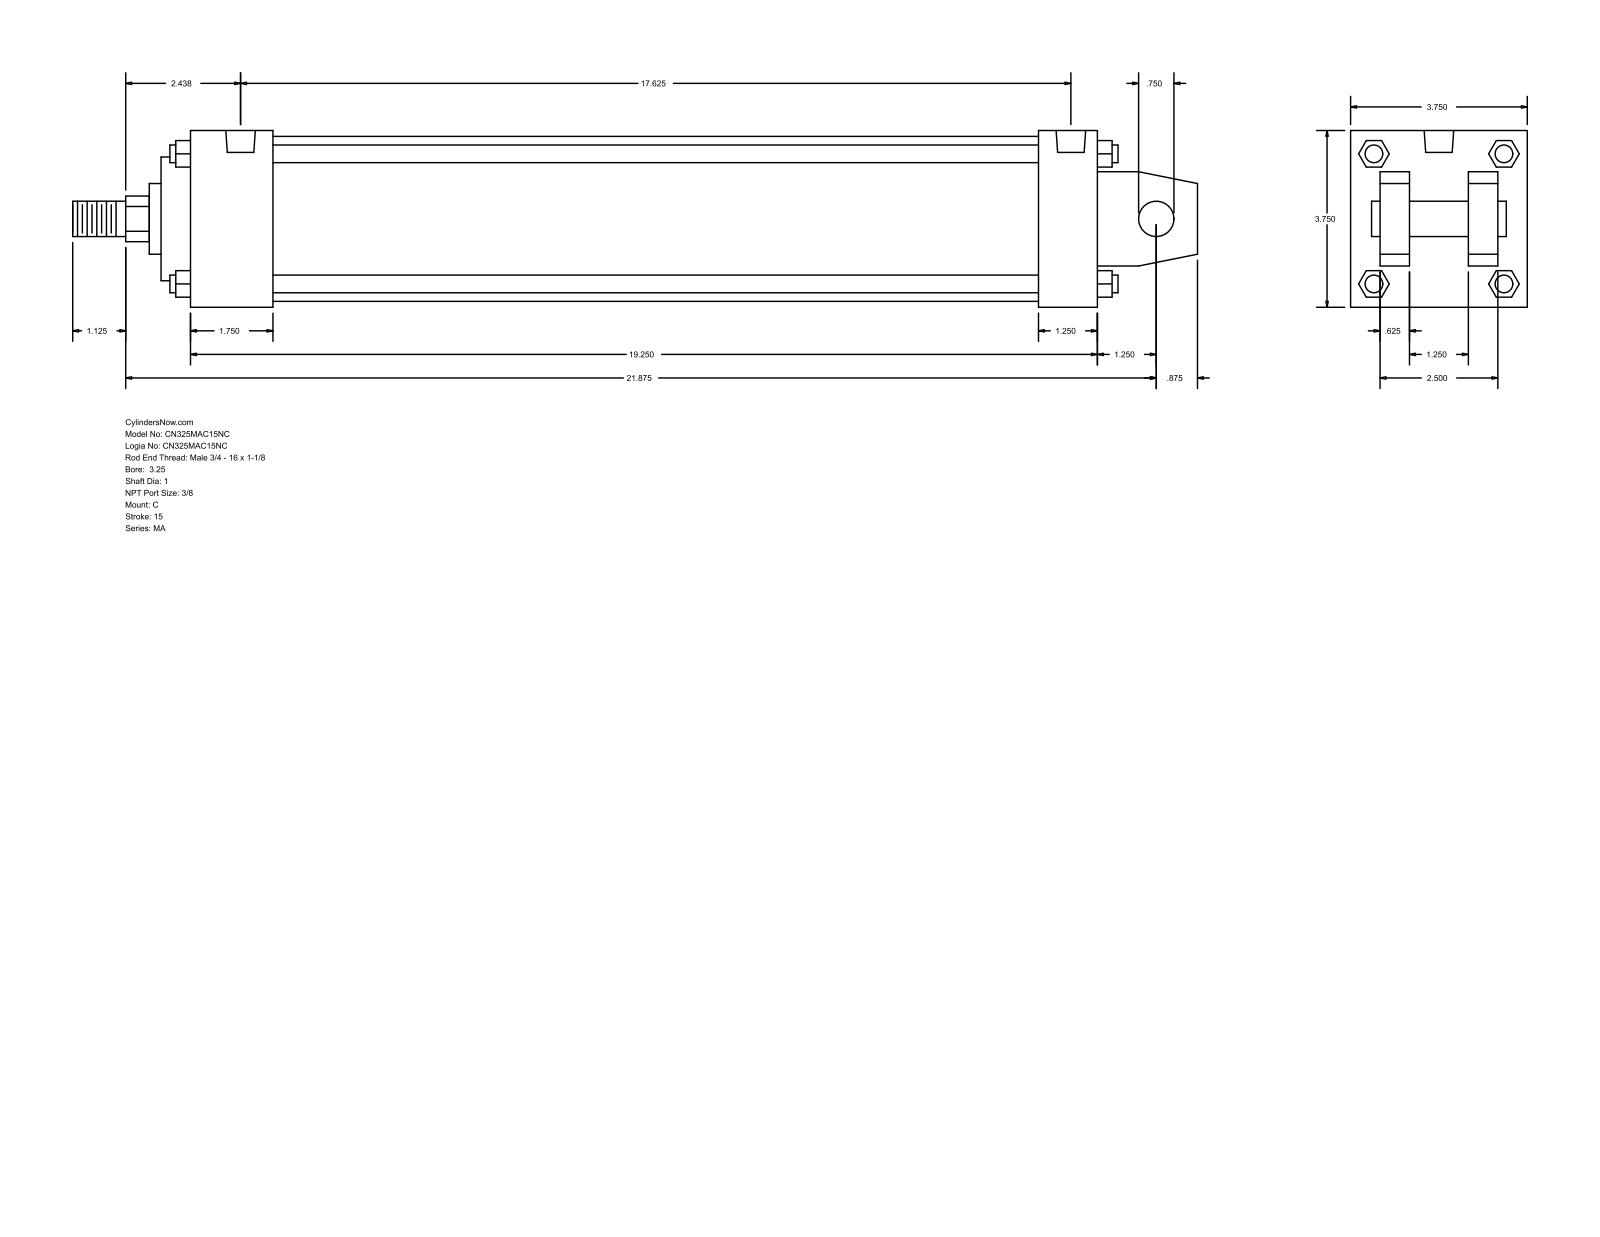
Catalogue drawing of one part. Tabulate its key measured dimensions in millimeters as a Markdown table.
| quantity | value |
| --- | --- |
| part name | MA_C__0325_1 |
| STEP written by | GSSL Pune (CONFIG_CONTROL_DESIGN) |
| units | millimeters |
| bodies | 0 solids, 141 faces (109 planar, 32 cylindrical, 0 other) |
| overall size | 606.42 × 95.25 × 95.25 |
| round holes (diameter × count) | 11.11 × 4, 15.93 × 2 |
| round bosses / shafts (diameter × count) | 9.53 × 4, 19.05 × 2, 88.9 × 1, 66.67 × 1, 38.1 × 1, 25.4 × 1 |
| partial cylindrical surfaces (radius × count) | 12.29 × 1 |
| main face-to-face distances | 95.24, 15.87, 63.5, 488.96, 31.76, 31.74, 79.37, 47.63, 457.2, 44.46 |
| hole center spacings | 438.15, 4.76, 4.77, 442.91, 442.92, 447.68 |
